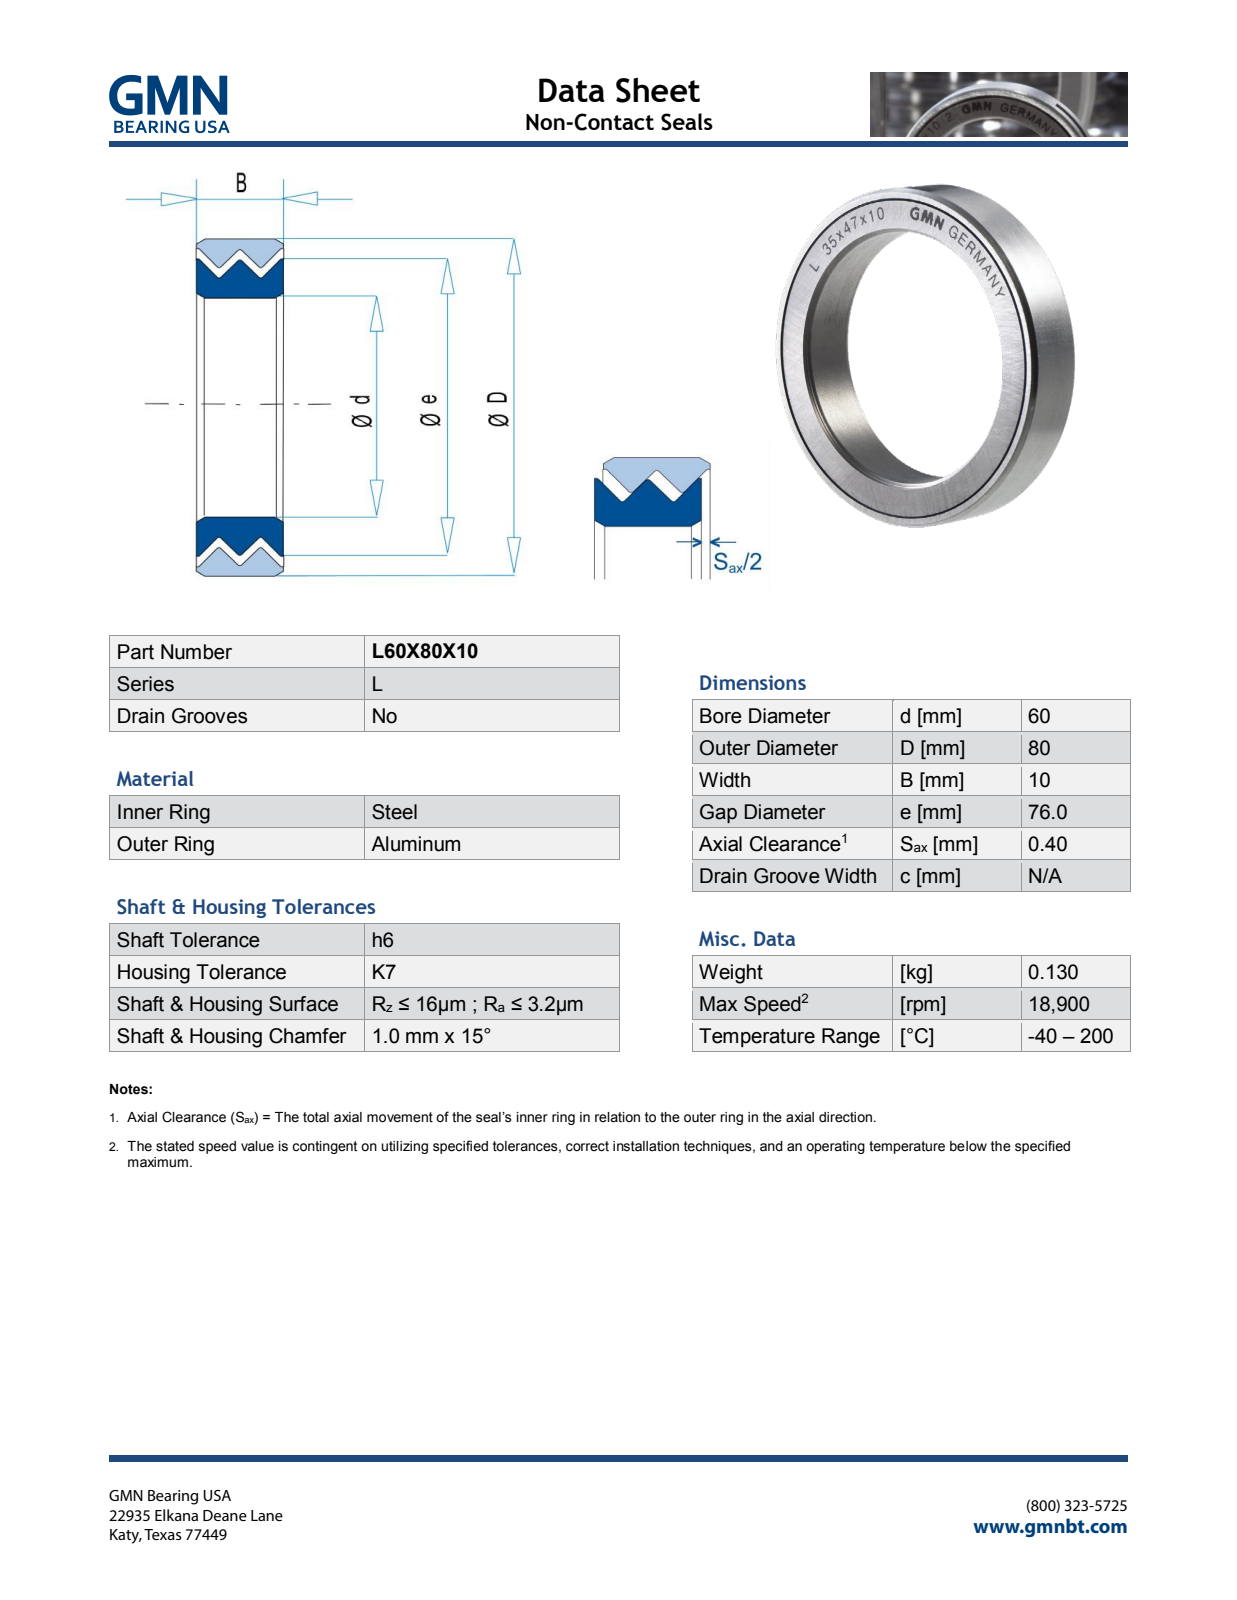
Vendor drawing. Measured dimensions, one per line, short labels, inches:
name: L60X80X10_PRT
written by: PRO/ENGINEER BY PARAMETRIC TECHNOLOGY CORPORATION, 2013150 (AUTOMOTIVE_DESIGN)
unit: in
bodies: 2 solids, 644 faces (588 planar, 12 cylindrical, 44 other)
size: 3.15 × 3.15 × 0.396
volume: 1.3 in³; area: 22.65 in²
holes: 1× ⌀2.362, 1× ⌀3.003
bosses: 1× ⌀3.15, 1× ⌀2.992
face distances: 0.394, 0.396, 0.027, 0.213, 0.027, 0.187, 0.16, 0.152, 0.187, 0.026
